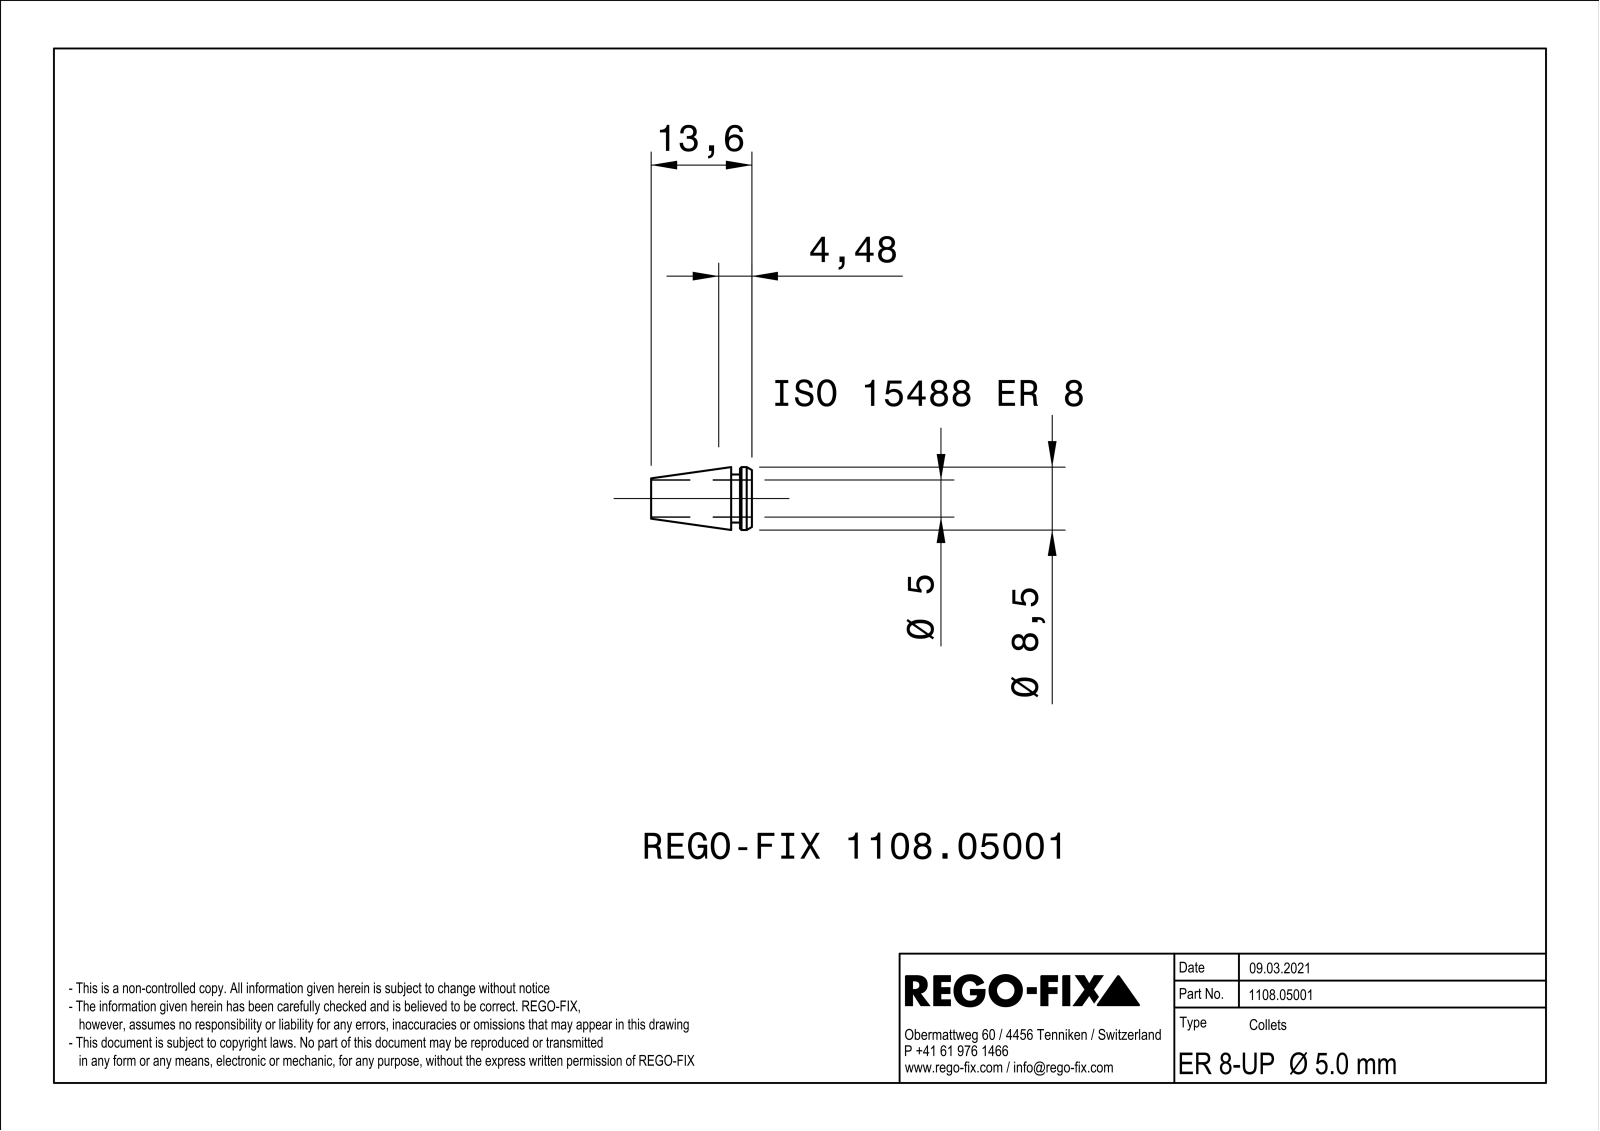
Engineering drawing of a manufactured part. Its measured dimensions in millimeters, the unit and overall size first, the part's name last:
Units: millimetres
Overall size (bounding box): 13.6 × 8.49 × 8.49
Round holes (diameter × count): ⌀5 ×1
Round bosses / shafts (diameter × count): ⌀8.5 ×1
Partial cylindrical surfaces — rounded edges, fillets, slot ends (radius × count): R20 ×6, R3.25 ×1
Main face-to-face distances: 0.4, 2.8, 1.6, 1.2
Volume: 216 mm³ · Surface area: 777 mm²
Bodies: 1 solid, 192 faces (66 planar, 42 cylindrical, 84 other)
Part name (STEP PRODUCT): NOCUT
STEP written by: SIEMENS PLM Software Solid Edge ST10 (AUTOMOTIVE_DESIGN)
